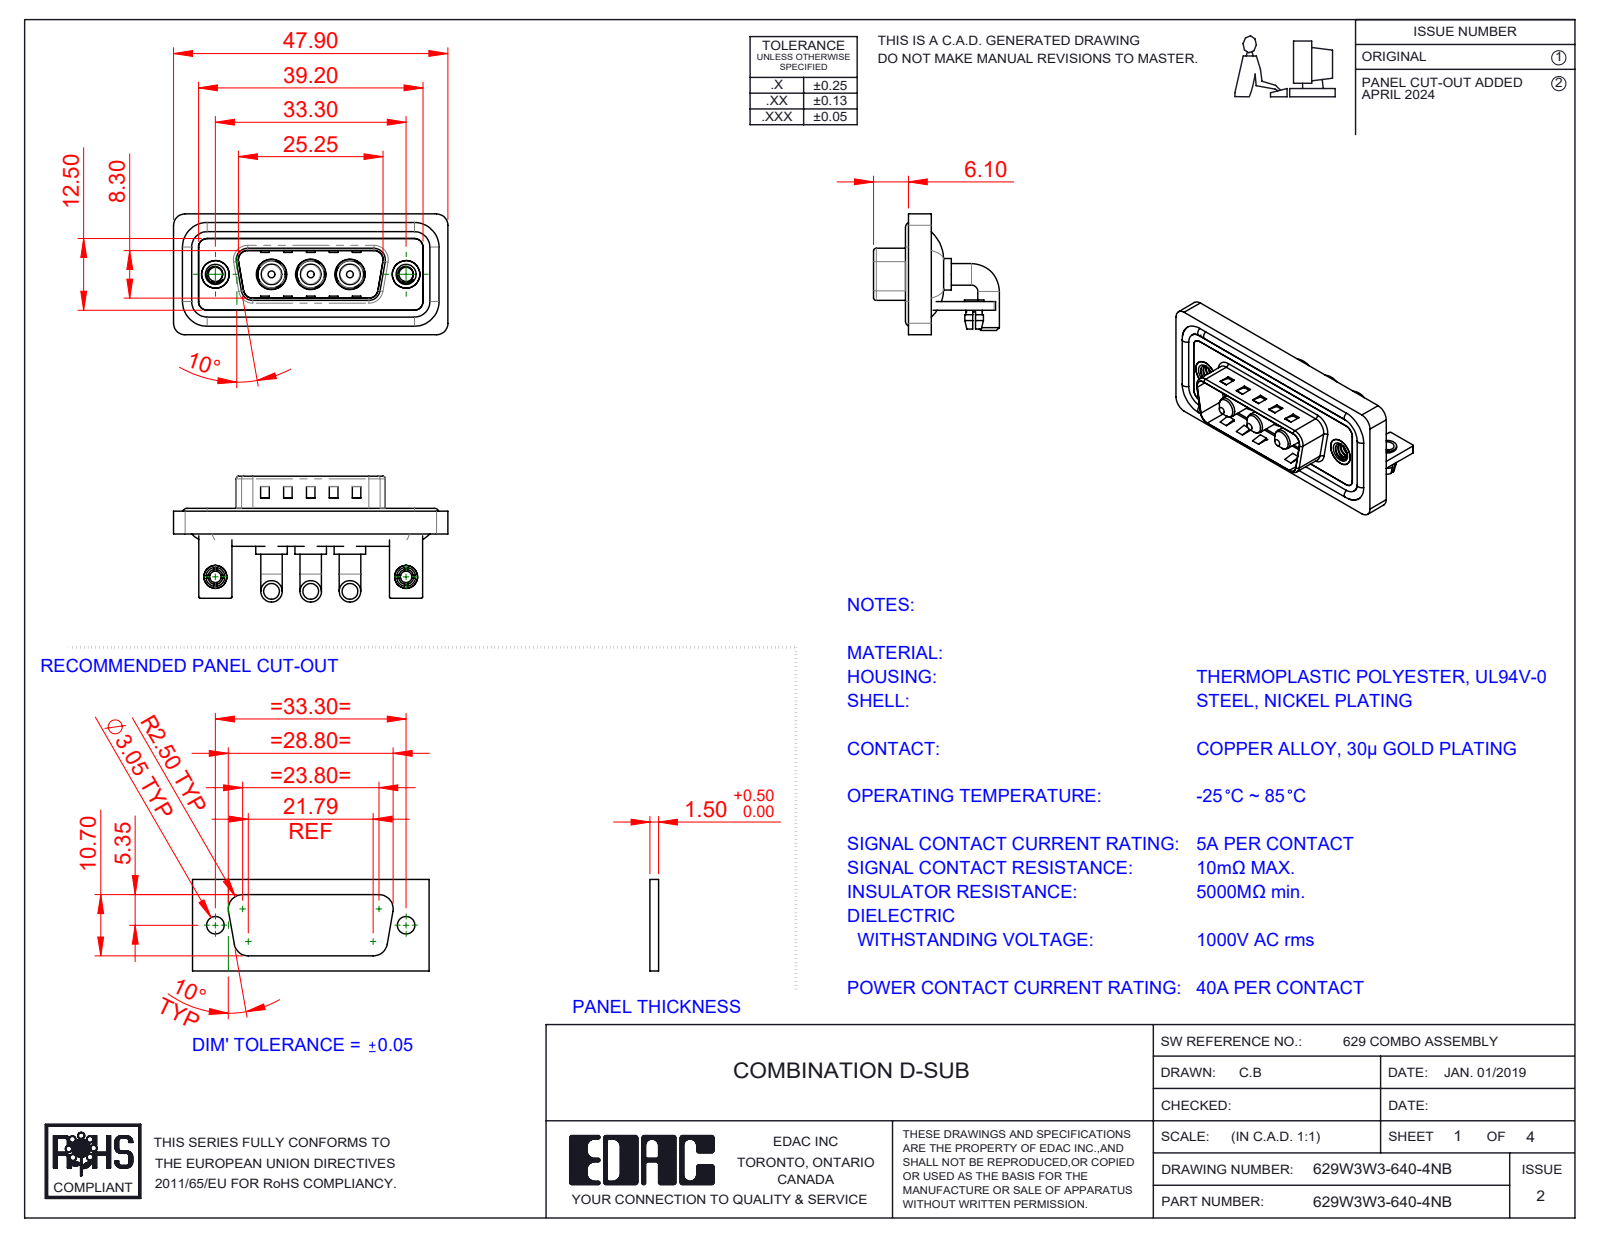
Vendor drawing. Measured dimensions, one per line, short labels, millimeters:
name: 629Combo Waterproof Housing_15 Contacts; 629W3W3-640-4NB; 629Combo Stabilizer Bracket; 629Combo Shell Rear_15 Contacts (+5 more)
written by: SolidWorks 2023 (CONFIG_CONTROL_DESIGN)
unit: mm
bodies: 17 solids, 706 faces (275 planar, 297 cylindrical, 134 other)
size: 47.9 × 21.98 × 21.1
volume: 6 305 mm³; area: 9 966 mm²
holes: 4× ⌀2.5, 3× ⌀4.85, 3× ⌀5.3, 2× ⌀2, 2× ⌀3.2, 2× ⌀4, 2× ⌀4.8, 2× ⌀5
bosses: 6× ⌀3.75, 4× ⌀1.6, 3× ⌀5.5, 3× ⌀5.2, 3× ⌀4.75, 3× ⌀3.6, 2× ⌀4.9, 2× ⌀4
rounds: 21× R2, 18× R1.5, 16× R0.25, 9× R0.5, 8× R1.6, 4× R0.6, 4× R0.65, 4× R0.9
face distances: 0.4, 1.5, 0.8, 2.9, 1.1, 2.1, 3.7, 1.6, 1.2, 4.5
hole spacings: 6.85, 9.8, 16.65, 23.5, 33.3, 13.7
